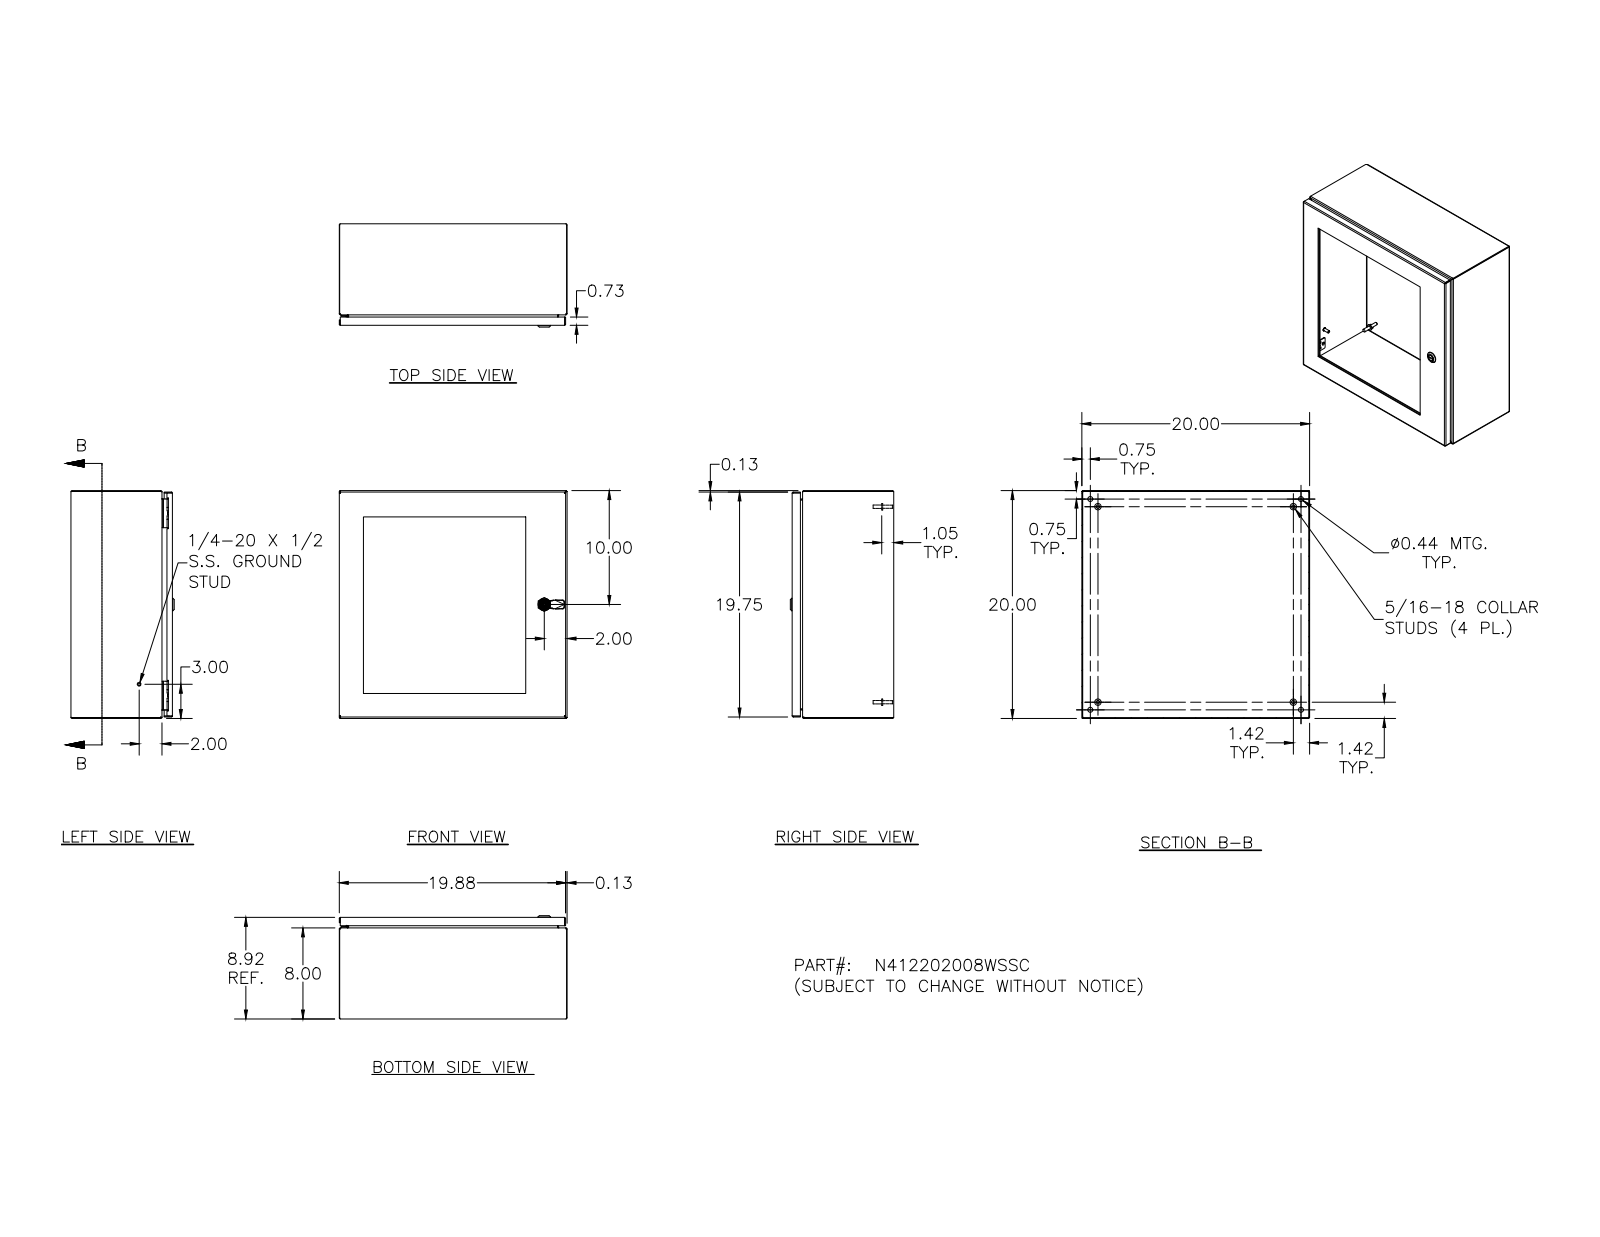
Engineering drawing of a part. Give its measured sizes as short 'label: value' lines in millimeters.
name: N412202008WSSC; N412202008WSSCBKP; N4122020WSSCLID; HFW328176 (+8 more)
written by: Autodesk Inventor 2011 (AUTOMOTIVE_DESIGN)
unit: mm
bodies: 70 solids, 1940 faces (754 planar, 565 cylindrical, 621 other)
size: 508 × 508 × 230.5
volume: 2 796 000 mm³; area: 2 235 000 mm²
holes: 18× ⌀4, 16× ⌀7.1, 4× ⌀2.4, 4× ⌀3.9, 4× ⌀4.2, 4× ⌀4.4, 4× ⌀4.8, 4× ⌀11.1, 1× ⌀4.7, 1× ⌀5, 1× ⌀8, 1× ⌀10
bosses: 16× ⌀4.8, 15× ⌀6.4, 10× ⌀6.4, 4× ⌀14.3, 4× ⌀9.1, 4× ⌀8.1, 4× ⌀7.6, 4× ⌀7
rounds: 34× R0.8, 26× R1.3, 24× R2.7, 18× R0.4, 16× R3.2, 9× R0.5, 8× R0.8, 4× R4
face distances: 1.9, 506.1, 224.6, 222.7, 504.2, 508, 6.4, 218.3, 216.4, 226.5
hole spacings: 101.6, 203.2, 406.6, 406.4, 437.4, 158, 218.1, 254.9
